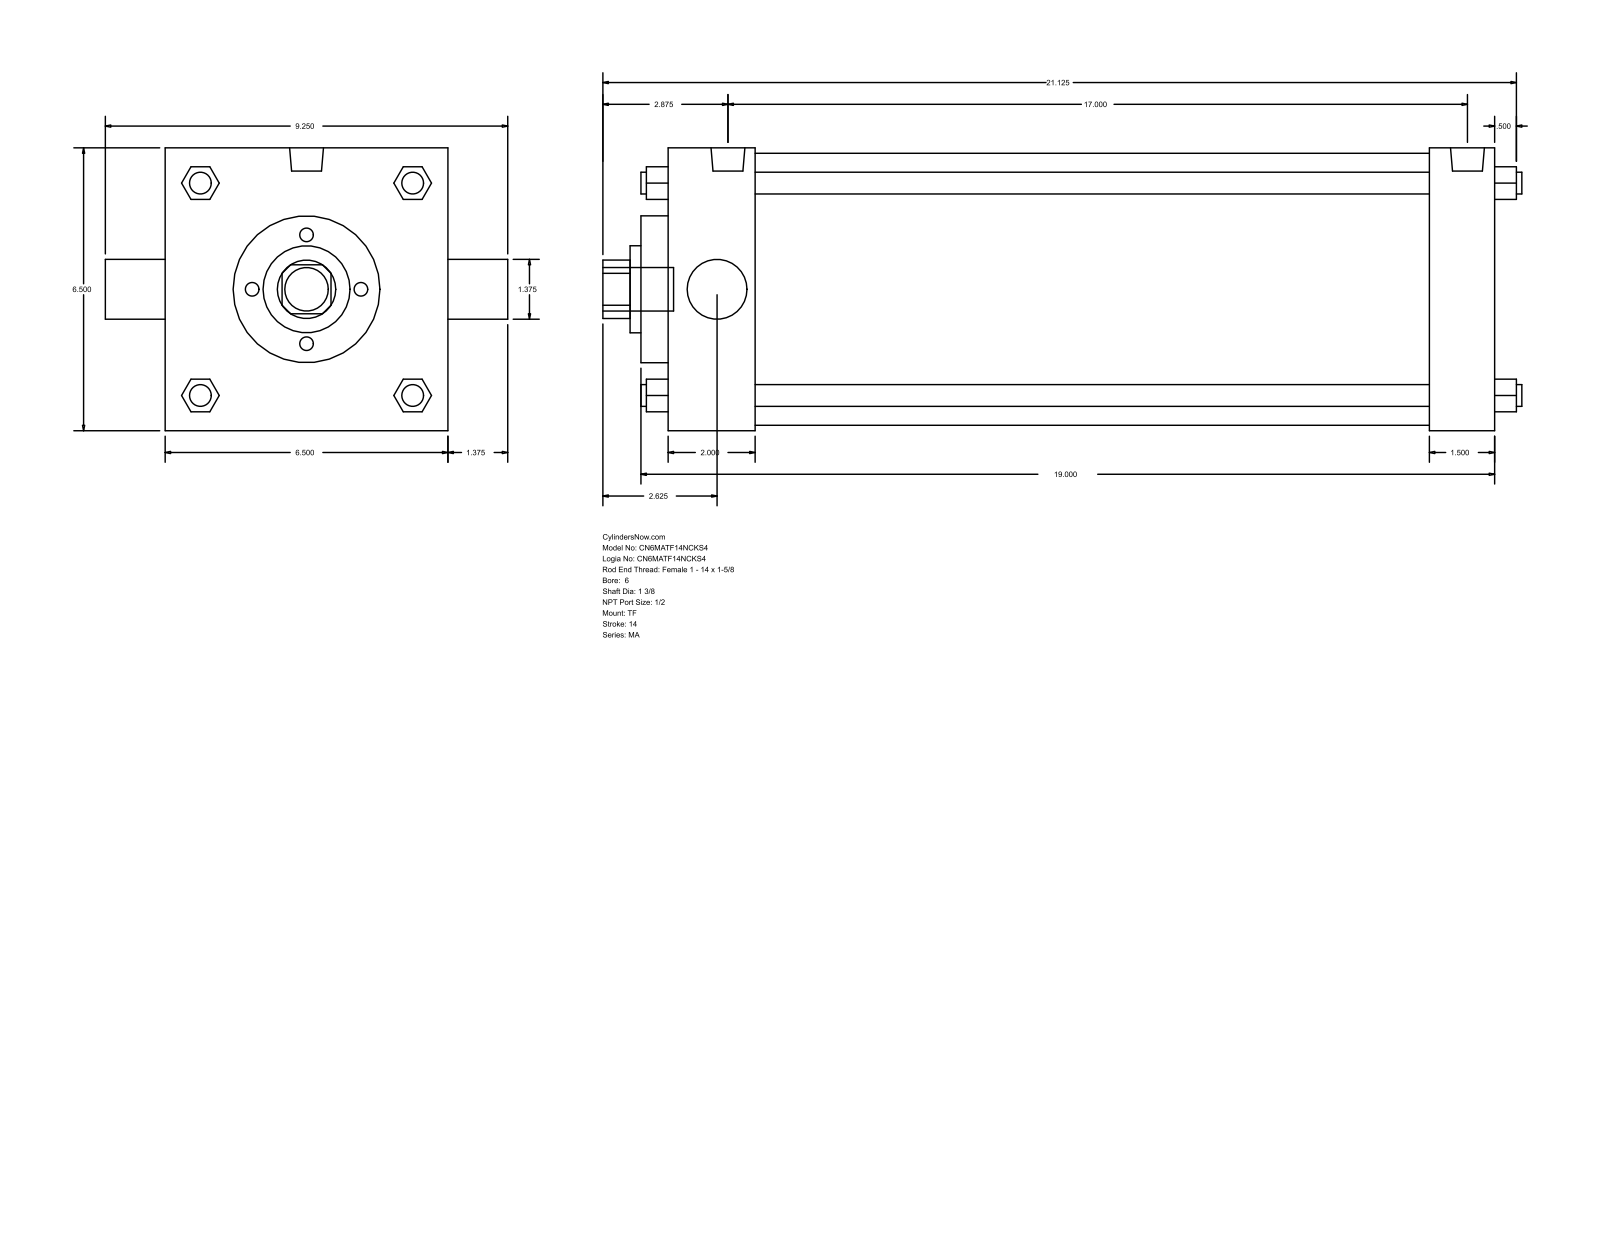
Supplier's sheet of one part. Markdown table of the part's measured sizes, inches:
| quantity | value |
| --- | --- |
| part name | MA_TF__0600_1.375 |
| STEP written by | GSSL Pune (CONFIG_CONTROL_DESIGN) |
| units | inches |
| bodies | 0 solids, 122 faces (93 planar, 29 cylindrical, 0 other) |
| overall size | 21.125 × 9.25 × 6.5 |
| round holes (diameter × count) | 1.375 × 2, 2 × 1, 3.375 × 1, 6.25 × 1 |
| round bosses / shafts (diameter × count) | 0.5 × 4, 0.687 × 3, 0.778 × 2, 1 × 1 |
| partial cylindrical surfaces (radius × count) | 0.672 × 1 |
| main face-to-face distances | 6.5, 19.125, 2, 17.125, 17.625, 15.625, 1.5, 0.625, 2.625, 18.25 |
